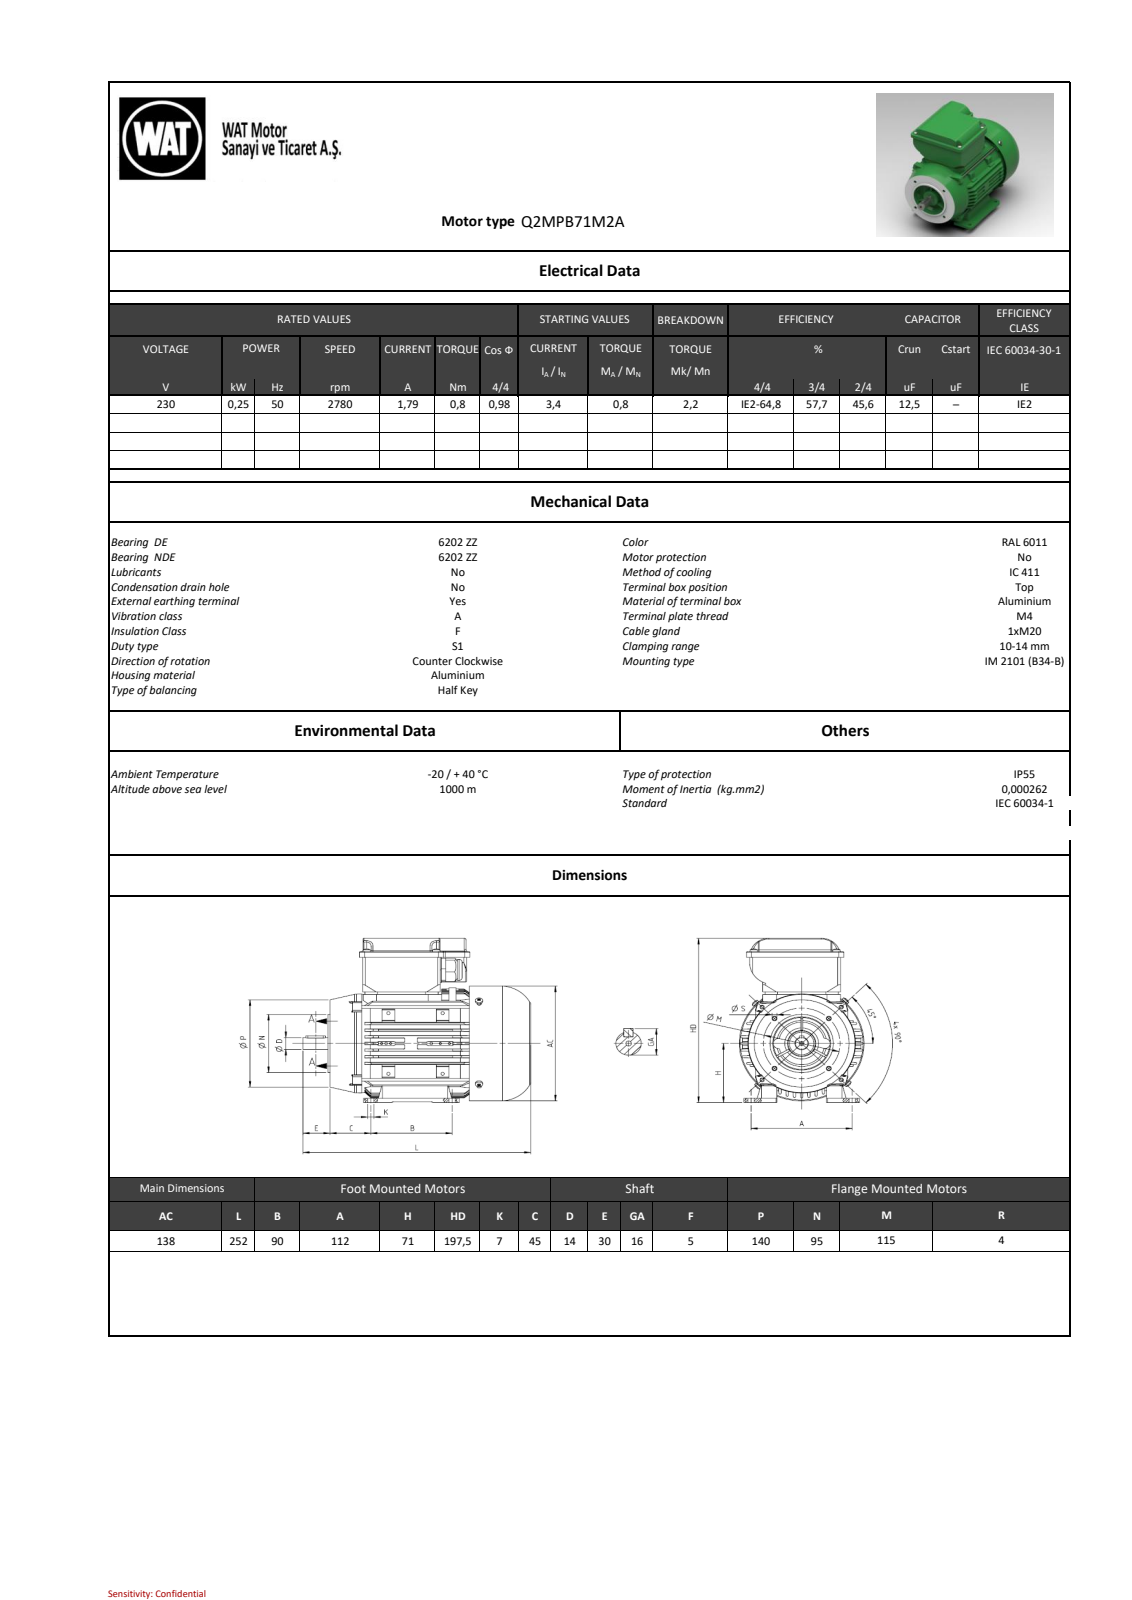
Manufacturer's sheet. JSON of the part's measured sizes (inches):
{"part_name": "BY6434017xx_004-TK_QM63-80; BY6424130xx_004-TKK_QM63-80; BY6422457xx_005-MOTOR_KAPAGI_QS71FB_ISLEME; 641304741_AZ-KAMA PARALEL A 5x5x22 St50 DIN6885 (+8 more)", "step_written_by": "SIEMENS PLM Software NX2206.8101 (AUTOMOTIVE_DESIGN)", "units": "inches", "bodies": {"solids": 26, "faces": 2704, "planar": 1299, "cylindrical": 751, "other": 654}, "overall_size": [9.921, 7.776, 5.531], "volume_in3": 50.72, "surface_area_in2": 773.5, "round_holes": [[0.13, 9], [0.144, 8], [0.177, 8], [0.098, 6], [0.315, 5], [0.157, 4], [0.183, 4], [0.189, 4], [0.205, 4], [0.276, 4], [0.118, 3], [0.146, 3]], "round_bosses_or_shafts": [[0.315, 8], [0.157, 8], [0.118, 8], [0.13, 4], [5.531, 1], [5.433, 1], [5.354, 1], [4.528, 1]], "partial_cylinders_radius": [[0.039, 119], [0.079, 79], [0.02, 38], [0.047, 36], [0.098, 14], [0.217, 13], [0.012, 12], [0.059, 12]], "face_to_face_distances": [0.118, 0.157, 7.303, 0.039, 2.657, 0.272, 1.264, 1.378, 5.768, 7.461], "hole_center_spacings": [3.326, 2.165, 1.441, 2.362, 0.172, 1.122, 1.467, 2.264]}
